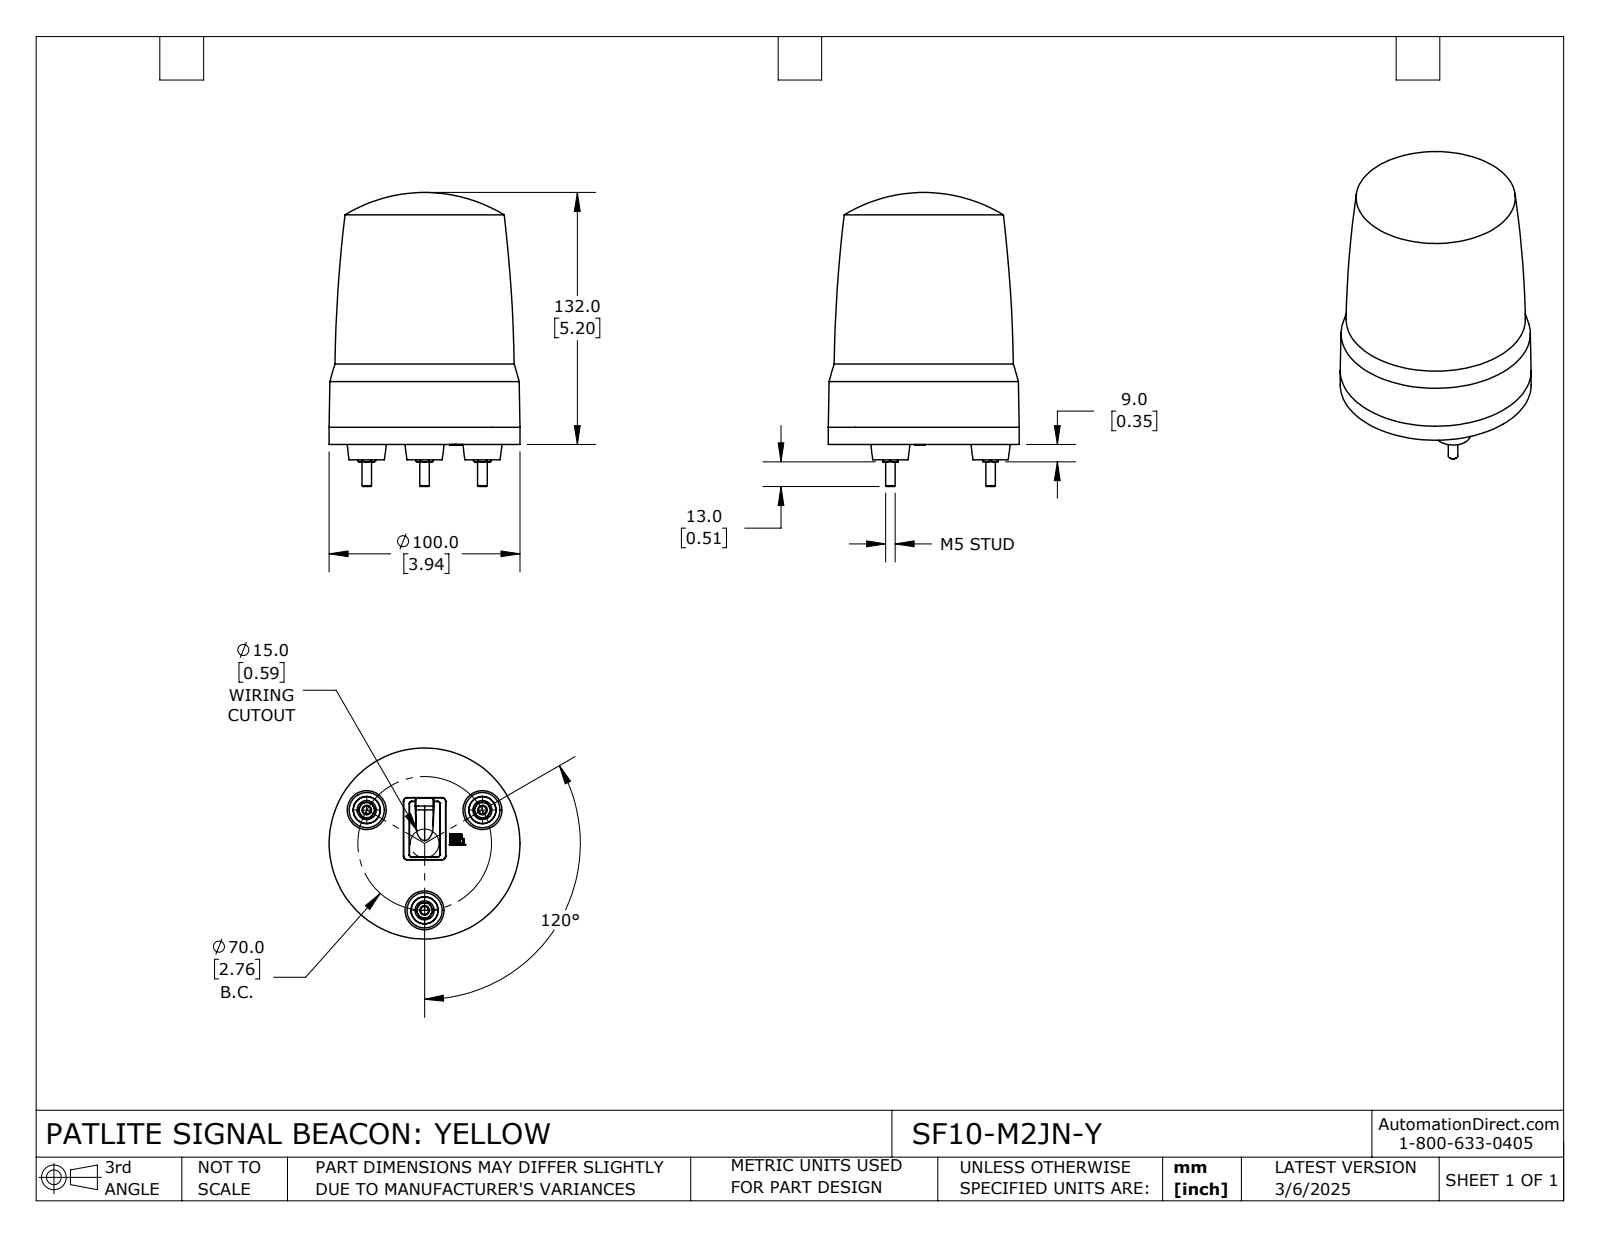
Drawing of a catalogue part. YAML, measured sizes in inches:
part_name: "SF10-M2JN-Y"
step_written_by: "SolidWorks 2024 (CONFIG_CONTROL_DESIGN)"
units: inches
bodies: {solids: 1, faces: 327, planar: 159, cylindrical: 14, other: 154}
overall_size: [6.063, 3.937, 3.937]
volume: 52.48
surface_area: 81.51
round_bosses_or_shafts:
  - {diameter: 0.394, count: 3}
  - {diameter: 0.197, count: 3}
  - {diameter: 3.937, count: 1}
face_to_face_distances: [0.315, 0.033, 0.348, 0.063, 0.411, 0.096, 0.15, 0.165, 0.199, 0.262]
